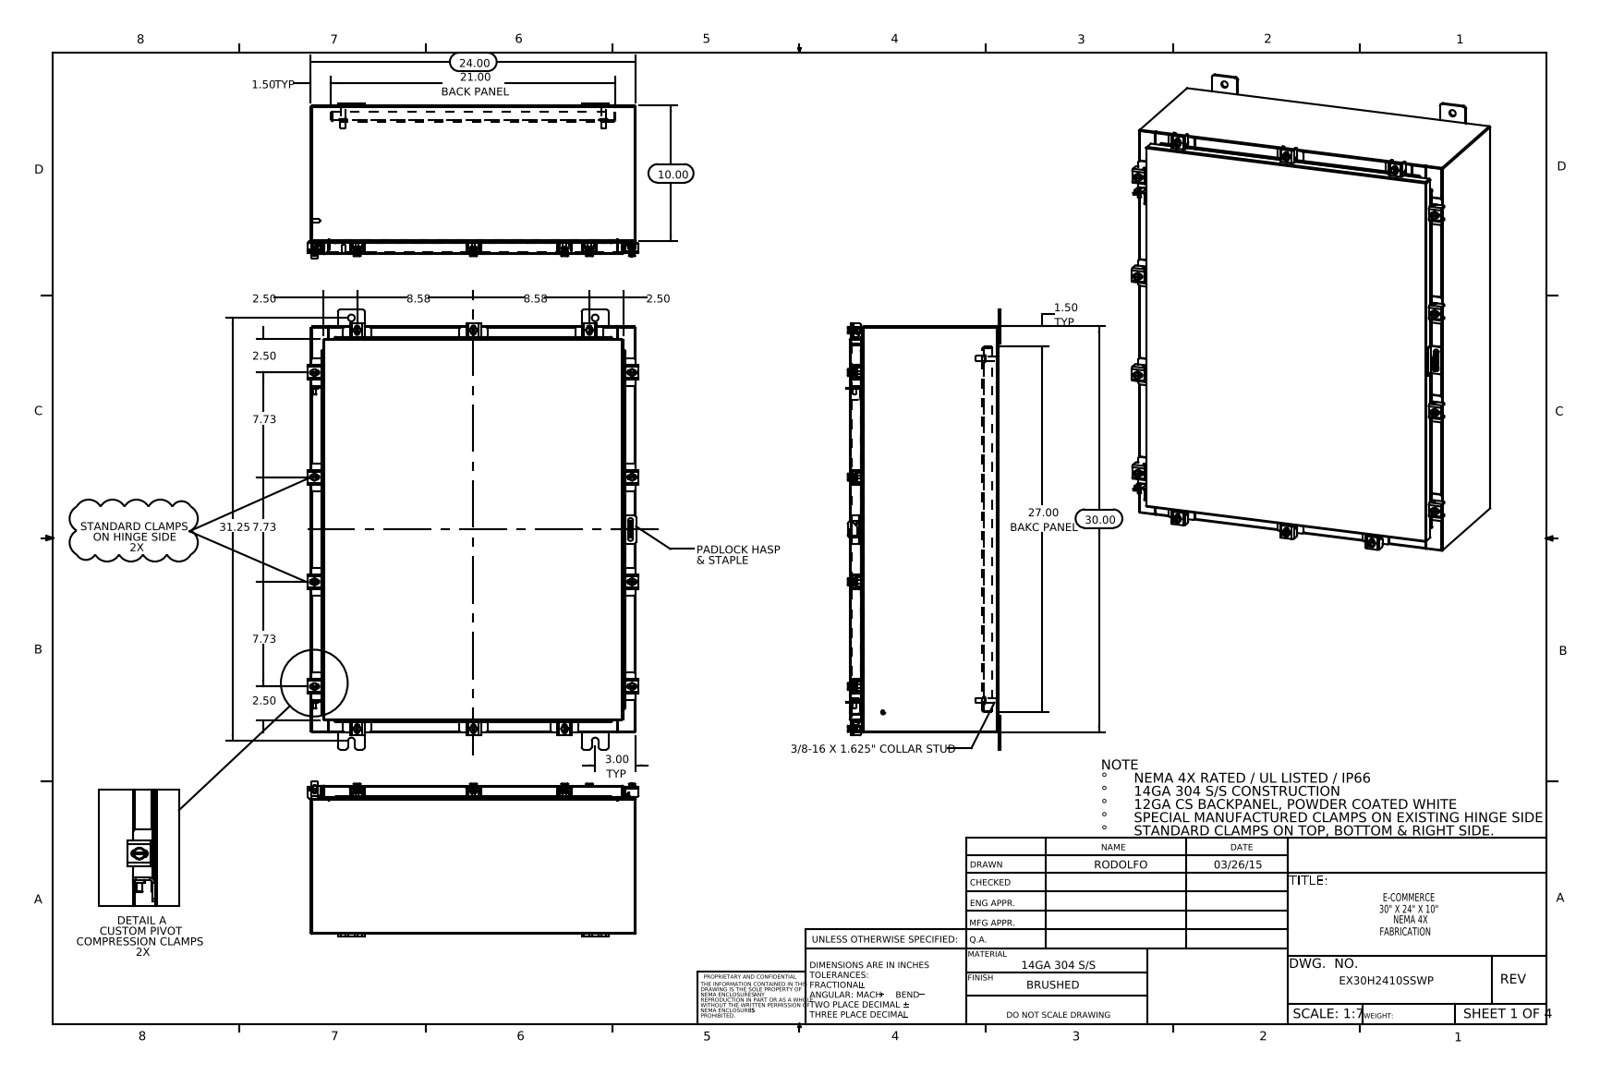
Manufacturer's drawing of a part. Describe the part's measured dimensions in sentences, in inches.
The part is named "Special Clamp Assembly; EX30H2410SSWP Top; EX30H2410SSWP Bottom; N-WMT04X30402202210-00 22101002 (+8 more)". Its 3-D file was written by "SolidWorks 2014 (CONFIG_CONTROL_DESIGN)". It is 91 solids with 2272 faces: 1211 planar, 885 cylindrical and 176 other. Overall it measures 32.5 by 24.421 by 11.453 inches. Its volume is 280.7 cubic inches and its surface area 7 003 square inches. Round holes: 14 of diameter 0.213, 14 of diameter 0.26, 8 of diameter 0.5, 1 of diameter 0.125, 1 of diameter 0.25. Round bosses or shafts: 14 of diameter 0.5, 14 of diameter 0.25, 12 of diameter 0.399, 4 of diameter 0.625, 4 of diameter 0.375, 4 of diameter 0.33, 2 of diameter 0.315, 2 of diameter 0.236. Partial cylindrical surfaces (rounded edges, fillets, slot ends): 62 of radius 0.06, 28 of radius 0.141, 26 of radius 0.013, 26 of radius 0.12, 24 of radius 0.19, 22 of radius 0.088, 22 of radius 0.09, 21 of radius 0.05. The main face-to-face distances are 0.075, 10.9, 10.975, 10.826, 0.104, 23.925, 1, 1.075, 9.826, 9.9. The hole center spacings are 23.451, 24.31, 32.286, 2.347, 4.44, 20.544, 26.507, 27.37.
